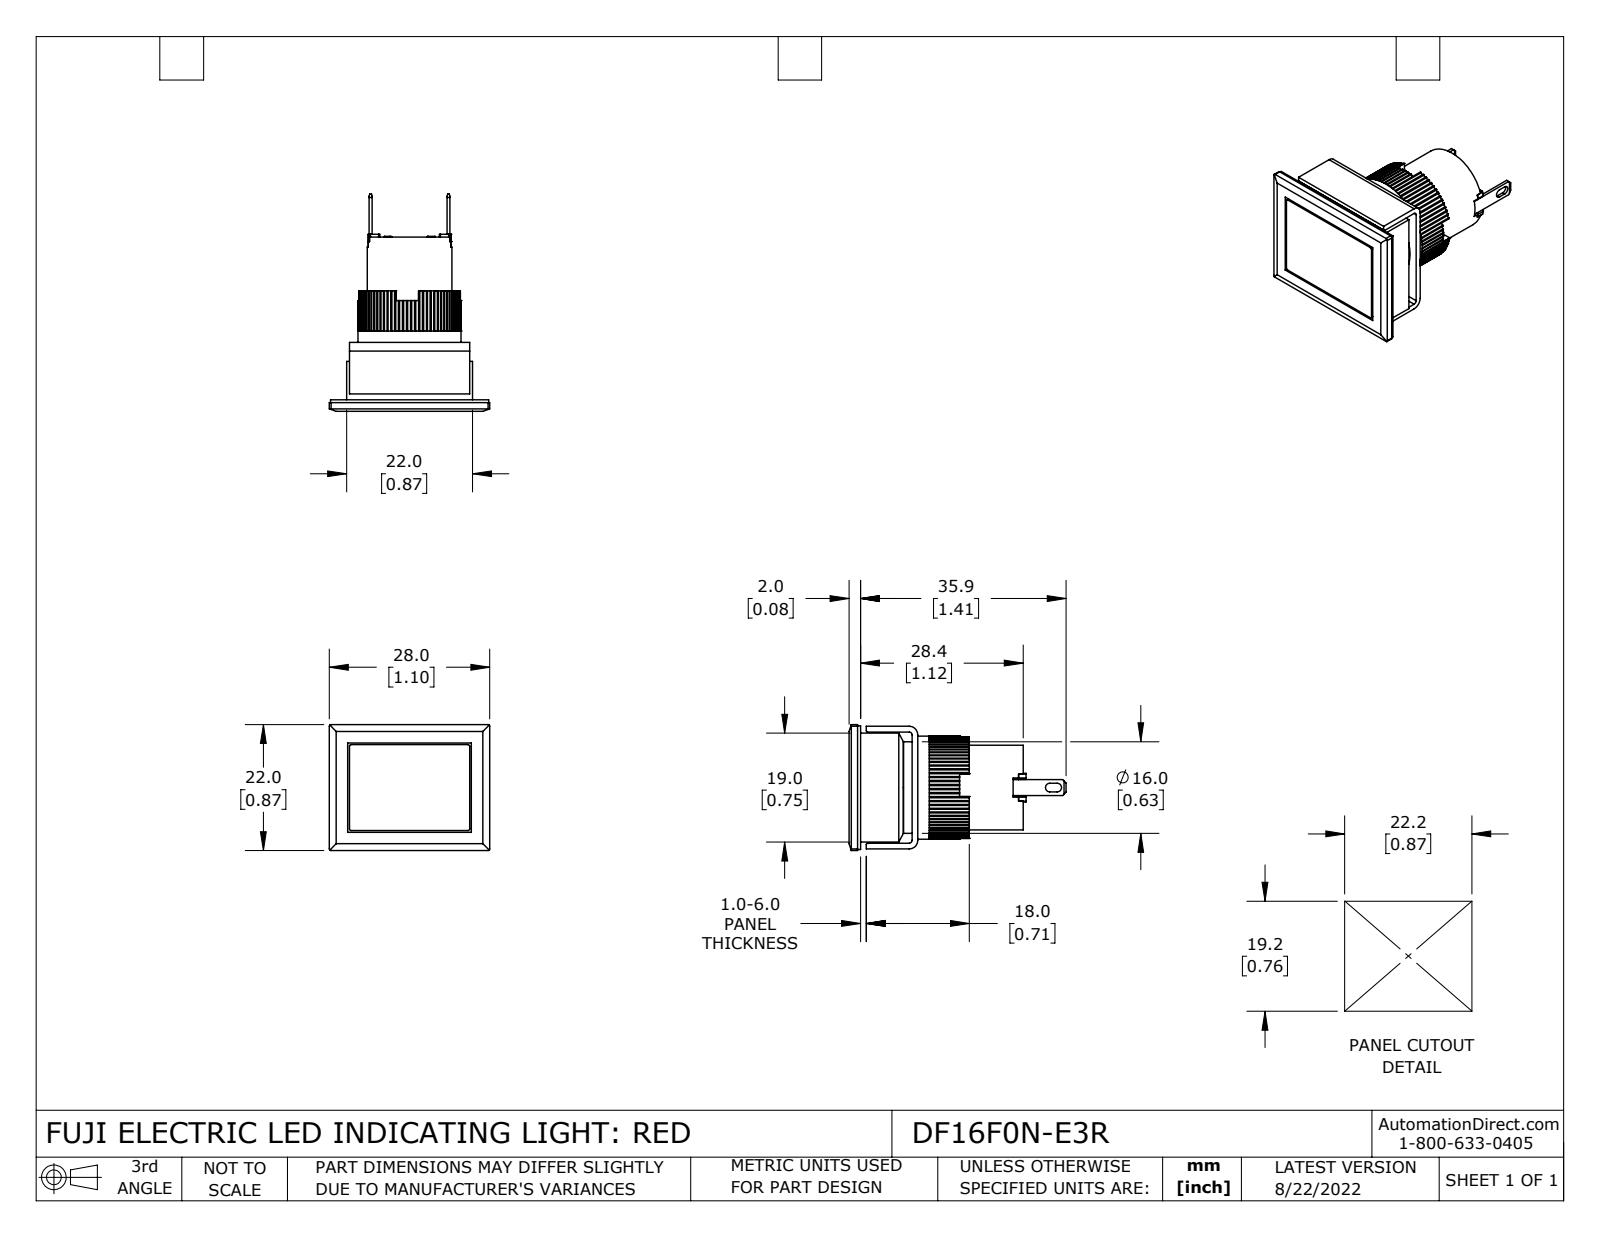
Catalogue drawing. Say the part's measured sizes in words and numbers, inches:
The part is named "DF16F0N-E3R". Its 3-D file was written by "SolidWorks 2021 (CONFIG_CONTROL_DESIGN)". It is 10 solids with 495 faces: 312 planar, 181 cylindrical and 2 other. Overall it measures 1.492 by 1.102 by 0.866 inches. Its volume is 0.546 cubic inches and its surface area 11.68 square inches. Round holes: 1 of diameter 0.039, 1 of diameter 0.709. Round bosses or shafts: 1 of diameter 0.63, 1 of diameter 0.583. Partial cylindrical surfaces (rounded edges, fillets, slot ends): 80 of radius 0.01, 12 of radius 0.008, 8 of radius 0.012, 2 of radius 0.02, 2 of radius 0.03, 2 of radius 0.059. The main face-to-face distances are 0.059, 0.374, 0.142, 0.02, 0.039, 0.315, 0.232, 0.083, 0.079, 0.756.
